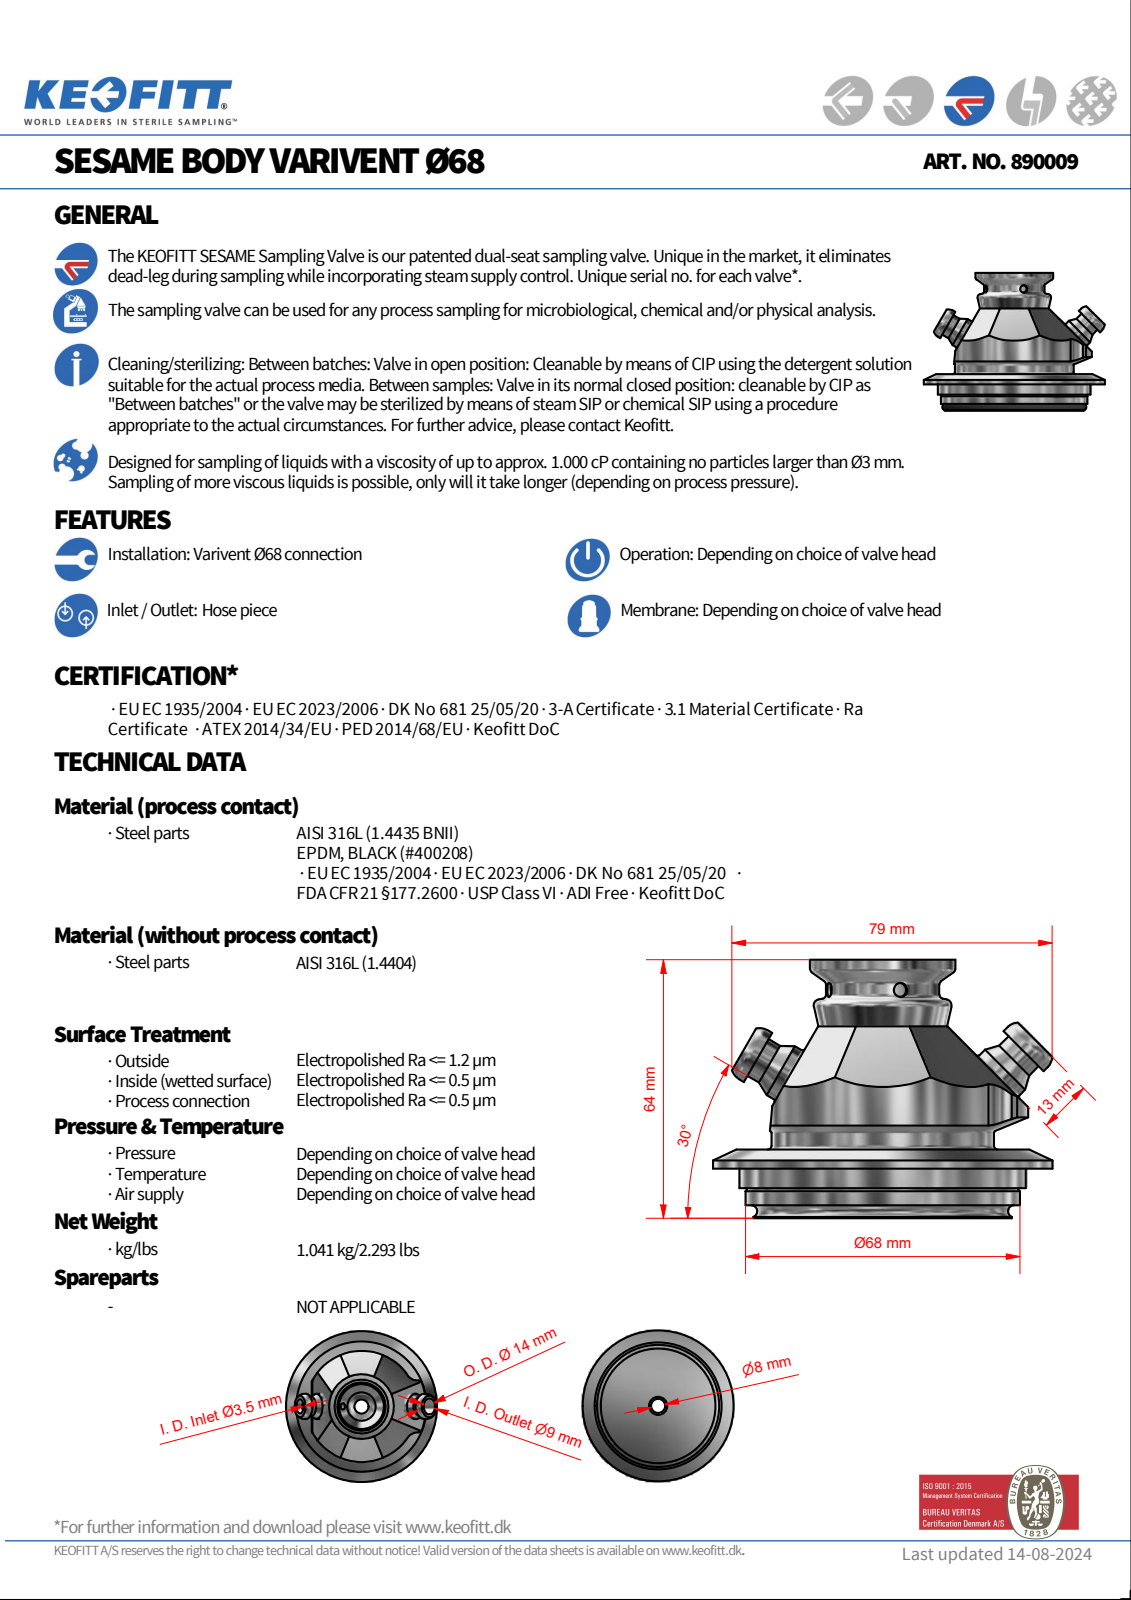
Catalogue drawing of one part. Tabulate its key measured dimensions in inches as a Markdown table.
| quantity | value |
| --- | --- |
| part name | 890009 |
| STEP written by | Autodesk Inventor 2020 (AUTOMOTIVE_DESIGN) |
| units | inches |
| bodies | 4 solids, 99 faces (28 planar, 37 cylindrical, 34 other) |
| overall size | 3.307 × 3.307 × 2.52 |
| volume | 8.768 in³ |
| surface area | 54.63 in² |
| round holes (diameter × count) | 0.138 × 3, 0.315 × 1, 0.354 × 1, 0.63 × 1, 0.984 × 1, 1.024 × 1, 1.142 × 1, 1.181 × 1 |
| round bosses / shafts (diameter × count) | 0.551 × 2, 0.413 × 2, 3.307 × 1, 2.789 × 1, 2.673 × 1, 2.516 × 1, 2.165 × 1, 1.417 × 1 |
| partial cylindrical surfaces (radius × count) | 0.276 × 2, 1.22 × 1, 1.417 × 1 |
| main face-to-face distances | 0.187, 0.482, 0.669, 0.354, 2.402, 1.919, 1.732, 0.295, 0.374, 2.106 |
